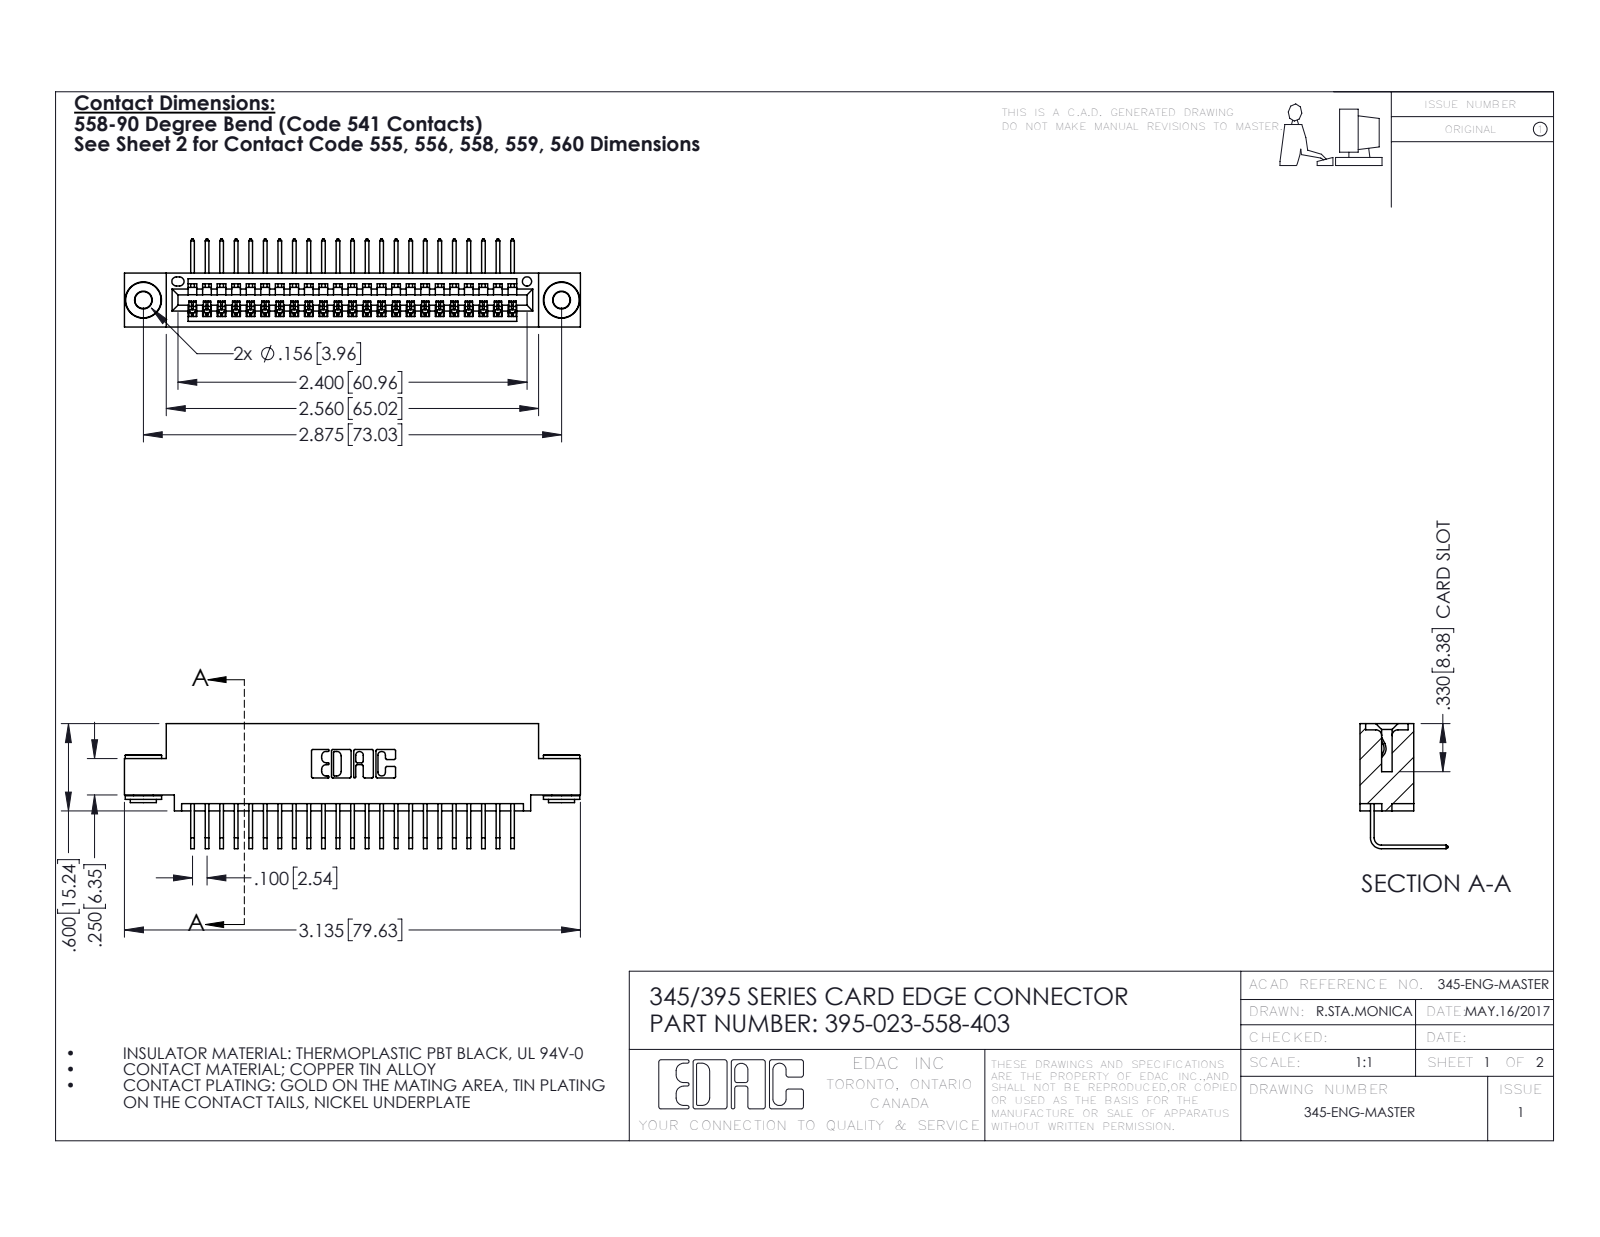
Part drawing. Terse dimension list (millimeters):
name: 345-250-002_345-250-002-102; 395-023-558-403; 345-292-001_558 Tail - 2; 345 Part_0.110 Offset - 0.156 Dia-TH
written by: SolidWorks 2016 (CONFIG_CONTROL_DESIGN)
unit: mm
bodies: 26 solids, 1548 faces (1060 planar, 480 cylindrical, 8 other)
size: 79.6 × 21.8 × 15.4
volume: 7 420 mm³; area: 10 360 mm²
holes: 2× ⌀2.9, 2× ⌀4, 1× ⌀1.6
bosses: 2× ⌀6.4, 2× ⌀4.6, 2× ⌀3.5
rounds: 46× R0.2, 22× R0.3, 6× R0.2, 6× R0.8, 3× R0.7, 2× R0.8, 2× R1, 1× R0.4
face distances: 1.8, 7.6, 9.4, 5.1, 0.6, 2.5, 6.9, 5.7, 3.8, 1.8
hole spacings: 6.9, 67.1, 73
